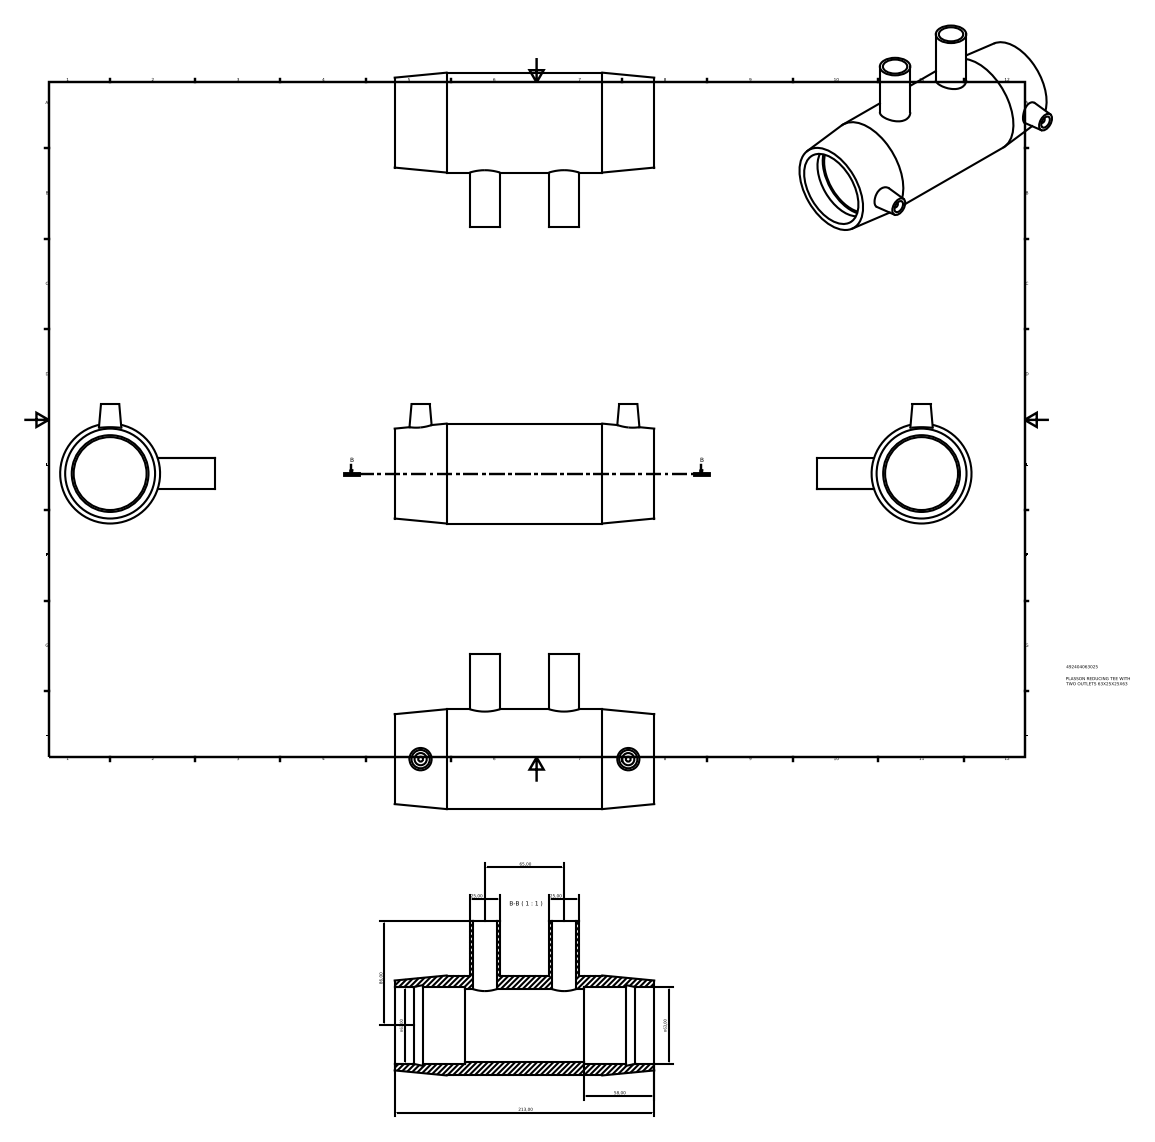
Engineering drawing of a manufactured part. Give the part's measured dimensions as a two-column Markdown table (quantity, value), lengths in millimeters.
| quantity | value |
| --- | --- |
| part name | 492404063025 |
| STEP written by | Autodesk Inventor 2015 (AUTOMOTIVE_DESIGN) |
| units | millimeters |
| bodies | 1 solid, 34 faces (14 planar, 14 cylindrical, 6 other) |
| overall size | 213 × 127 × 98 |
| volume | 459 502 mm³ |
| surface area | 114 842 mm² |
| round holes (diameter × count) | 10 × 2, 20 × 2, 59.85 × 1, 63 × 1 |
| round bosses / shafts (diameter × count) | 25 × 2, 4 × 2, 82 × 1 |
| main face-to-face distances | 213, 23.2, 189.8, 58, 155, 34.8, 131.8, 166.6, 97, 14 |
| hole center spacings | 65, 170.4 |
